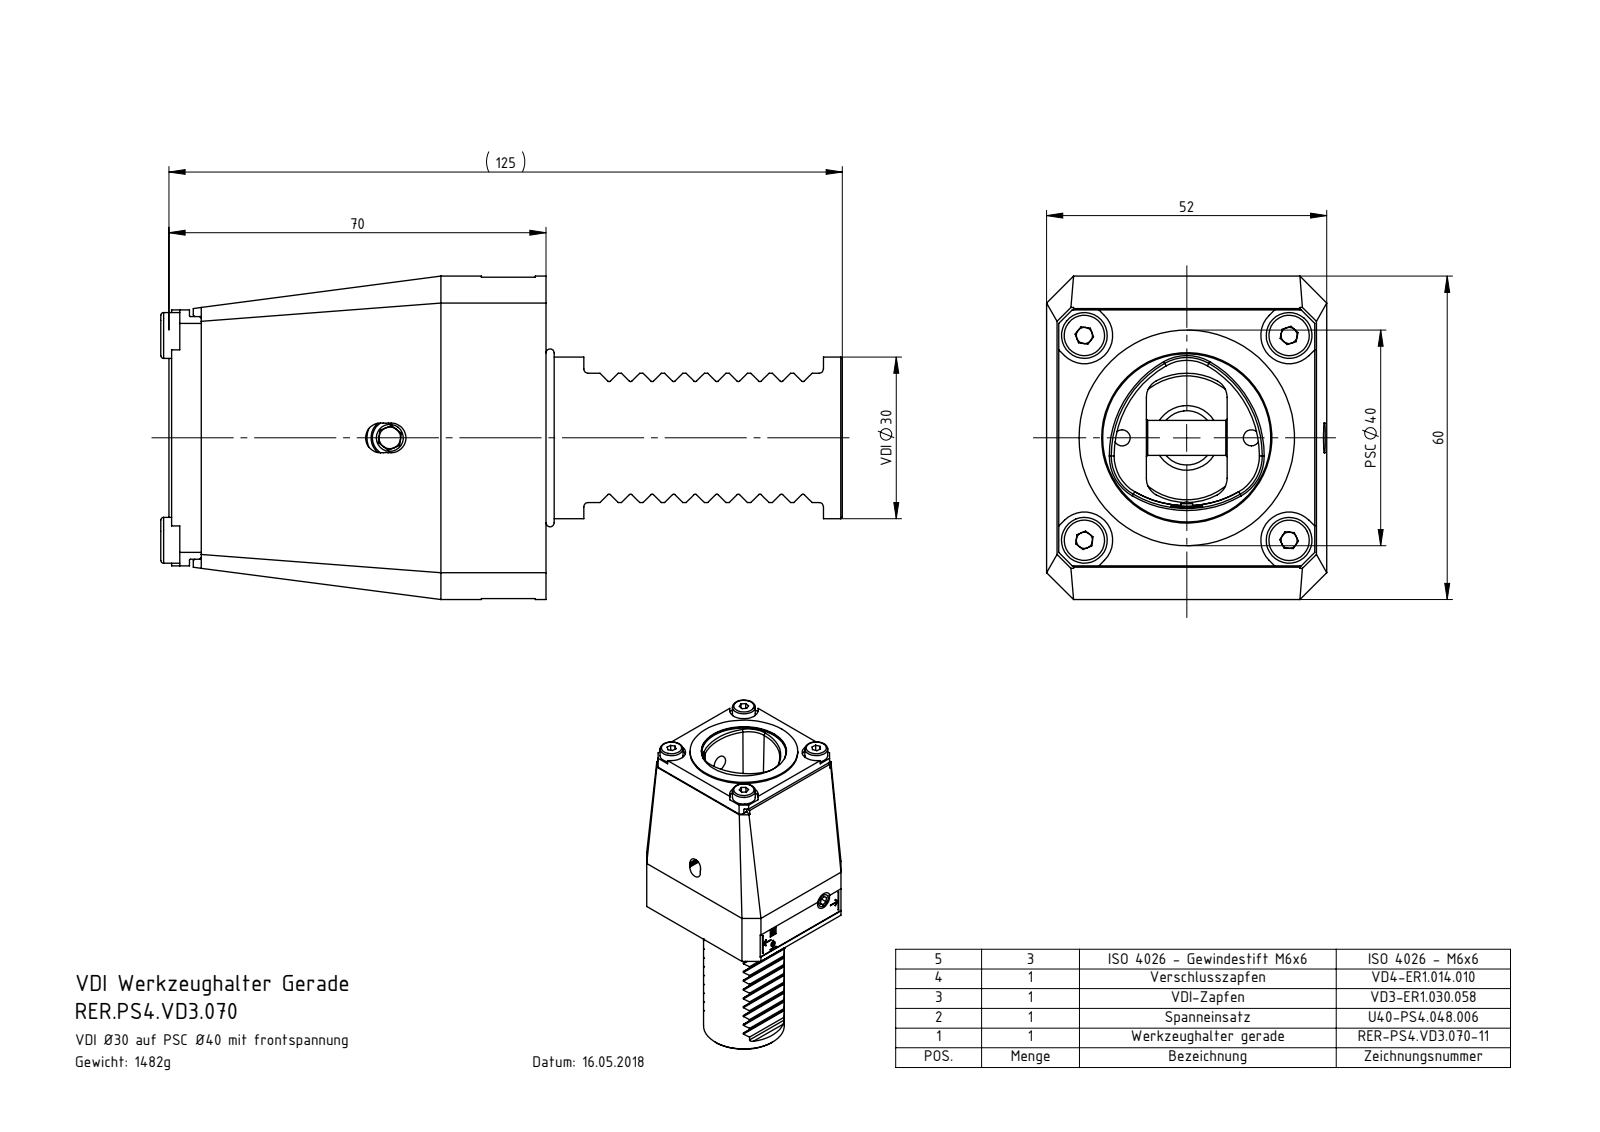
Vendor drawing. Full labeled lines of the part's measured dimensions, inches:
Part name (STEP PRODUCT): VD4-ER1.014.010; VD3-ER1.030.058; VD3-ER1.030.058_B; RER-PS4.VD3.070-11_B (+8 more)
STEP written by: SolidWorks 2022 (AUTOMOTIVE_DESIGN)
Units: inches
Bodies: 26 solids, 949 faces (410 planar, 226 cylindrical, 313 other)
Overall size (bounding box): 4.98 × 2.362 × 2.047
Volume: 11.69 in³ · Surface area: 105.4 in²
Round holes (diameter × count): ⌀0.197 ×5, ⌀0.098 ×4, ⌀0.165 ×4, ⌀0.217 ×4, ⌀0.512 ×3, ⌀0.118 ×2, ⌀0.13 ×2, ⌀0.157 ×1, ⌀0.236 ×1, ⌀0.276 ×1, ⌀0.402 ×1, ⌀0.551 ×1
Round bosses / shafts (diameter × count): ⌀0.335 ×4, ⌀0.197 ×4, ⌀0.236 ×3, ⌀0.217 ×2, ⌀0.118 ×2, ⌀1.575 ×1, ⌀1.563 ×1, ⌀1.488 ×1
Partial cylindrical surfaces — rounded edges, fillets, slot ends (radius × count): R0.012 ×20, R0.031 ×4, R0.108 ×4, R0.138 ×4, R0.207 ×4, R0.008 ×2, R0.118 ×2, R0.354 ×1
Main face-to-face distances: 1.654, 0.866, 1.87, 2.52, 0.111, 0.118, 2.402, 2.047, 0.079, 0.748
Hole centre spacings: 0.797, 1.058, 1.431, 1.496, 0.276, 0.472, 0.5, 0.621
